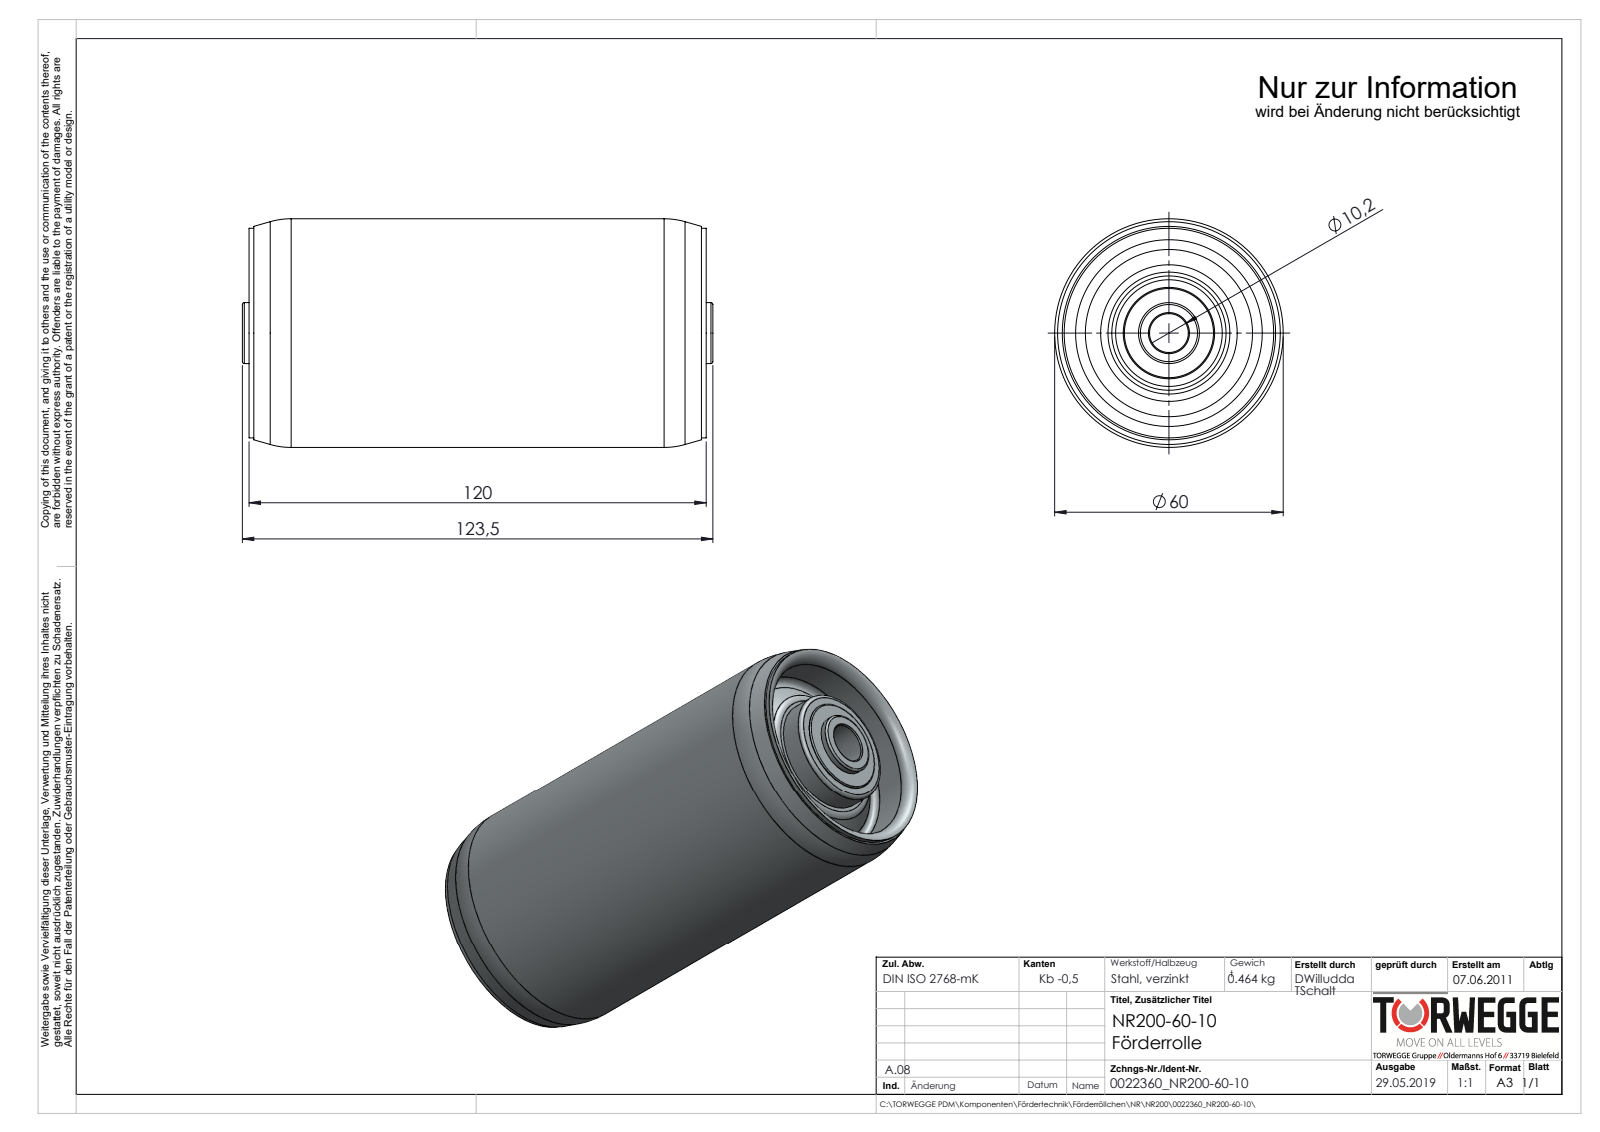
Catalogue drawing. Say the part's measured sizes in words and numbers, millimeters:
The part is named "0022360_NR200-60-10_(A-14)". Its 3-D file was written by "SolidWorks 2018 (AUTOMOTIVE_DESIGN)". It is 1 solid with 122 faces: 18 planar, 40 cylindrical and 64 other. Overall it measures 123.5 by 60 by 60 millimeters. Its volume is 58 949 cubic millimeters and its surface area 70 779 square millimeters. Round holes: 1 of diameter 10.2, 1 of diameter 20.7, 1 of diameter 26.7, 1 of diameter 49, 1 of diameter 56.7. Round bosses or shafts: 1 of diameter 60, 1 of diameter 55, 1 of diameter 52.3, 1 of diameter 30, 1 of diameter 24, 1 of diameter 16, 1 of diameter 13.5. The main face-to-face distances are 0.5, 1.65, 117.35, 116.85, 110.85, 2.15, 6.5, 7, 110.35, 1.15.
